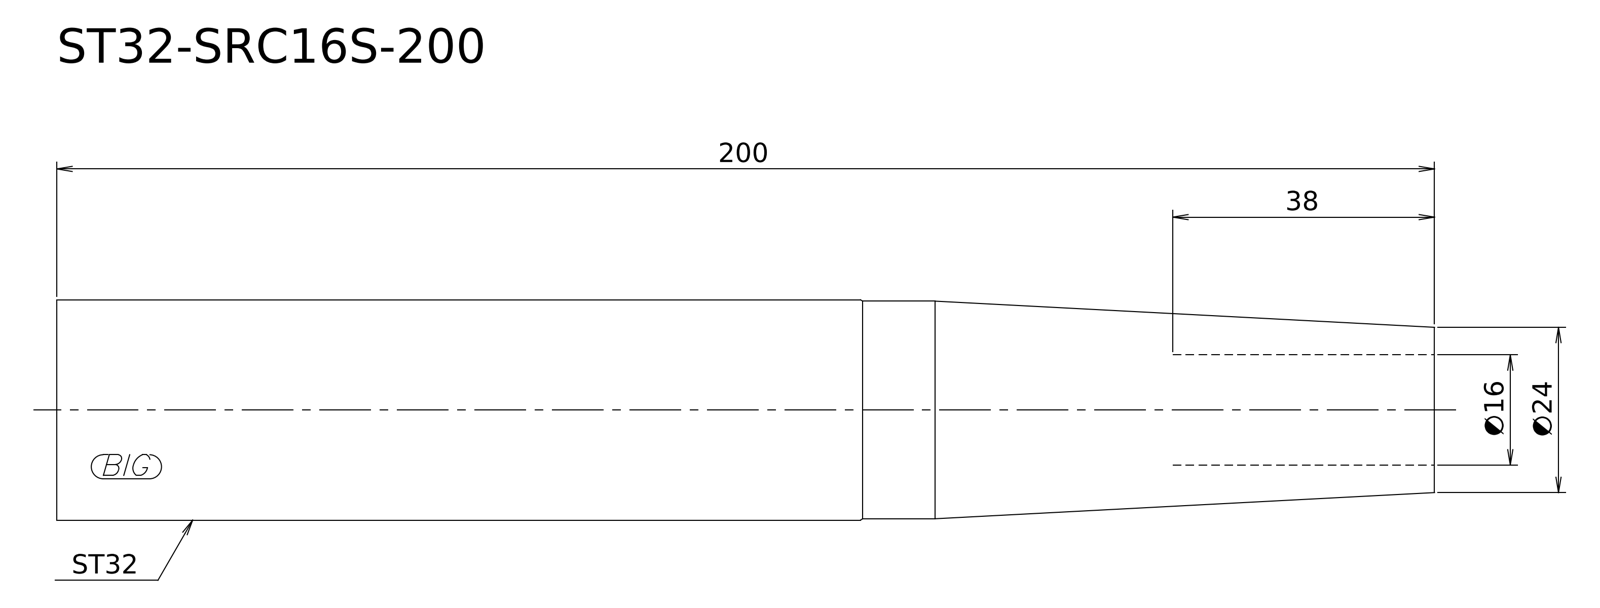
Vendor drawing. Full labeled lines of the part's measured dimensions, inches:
STEP written by: Kubotek KeyCreator V8.5.1 (14335) (CONFIG_CONTROL_DESIGN)
Units: inches
Bodies: 1 solid, 6 faces (2 planar, 2 cylindrical, 2 other)
Overall size (bounding box): 7.874 × 1.26 × 1.26
Volume: 8.947 in³ · Surface area: 31.63 in²
Round bosses / shafts (diameter × count): ⌀1.26 ×1, ⌀1.244 ×1
Main face-to-face distances: 7.874
